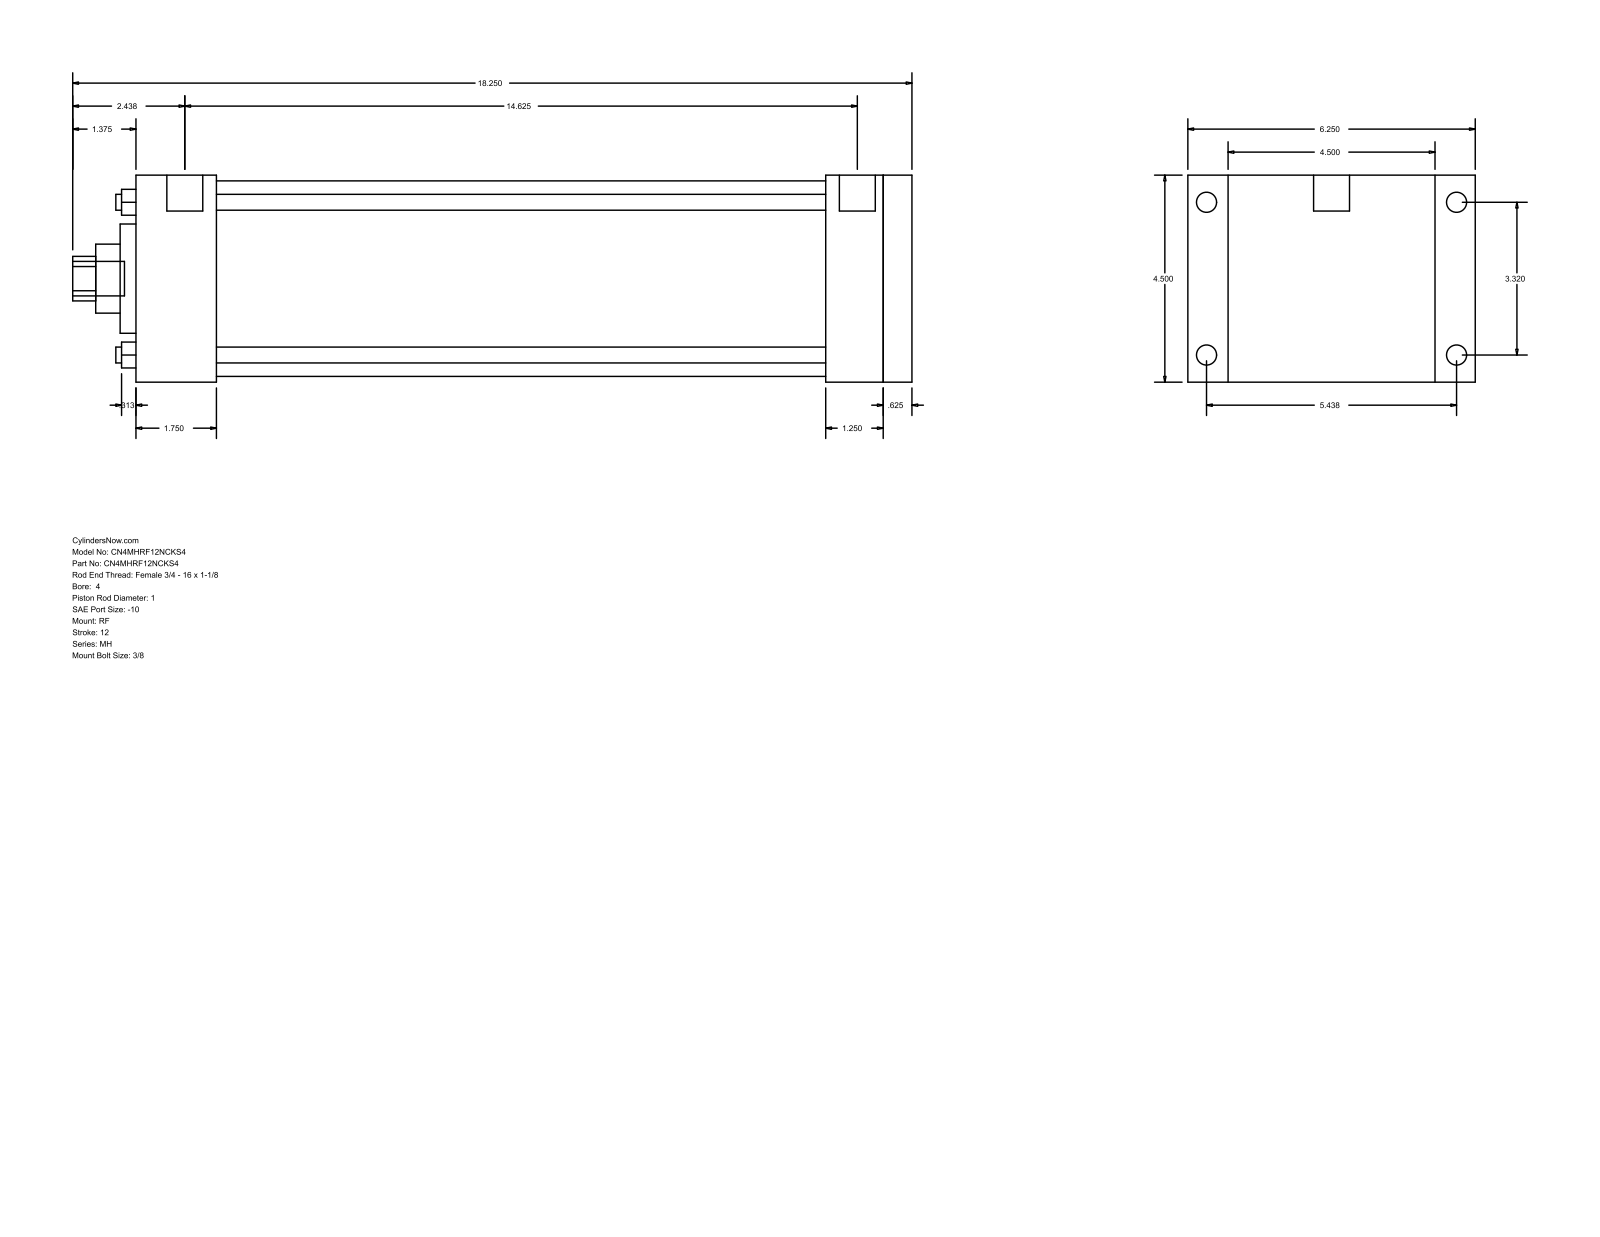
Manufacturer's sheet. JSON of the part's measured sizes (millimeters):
{"part_name": "MH_RF__0400_1", "step_written_by": "GSSL Pune (CONFIG_CONTROL_DESIGN)", "units": "millimeters", "bodies": {"solids": 0, "faces": 94, "planar": 65, "cylindrical": 29, "other": 0}, "overall_size": [463.55, 158.75, 114.3], "round_holes": [[8.76, 4], [25.4, 1], [38.1, 1], [60.33, 1], [107.95, 1]], "round_bosses_or_shafts": [[11.13, 4], [8.73, 4], [19.84, 2], [19.05, 1]], "partial_cylinders_radius": [[12.29, 1]], "face_to_face_distances": [114.3, 428.63, 15.87, 412.76, 44.46, 368.3, 384.17, 381.01, 336.55, 31.75], "hole_center_spacings": [59.62, 84.32, 119.25]}
